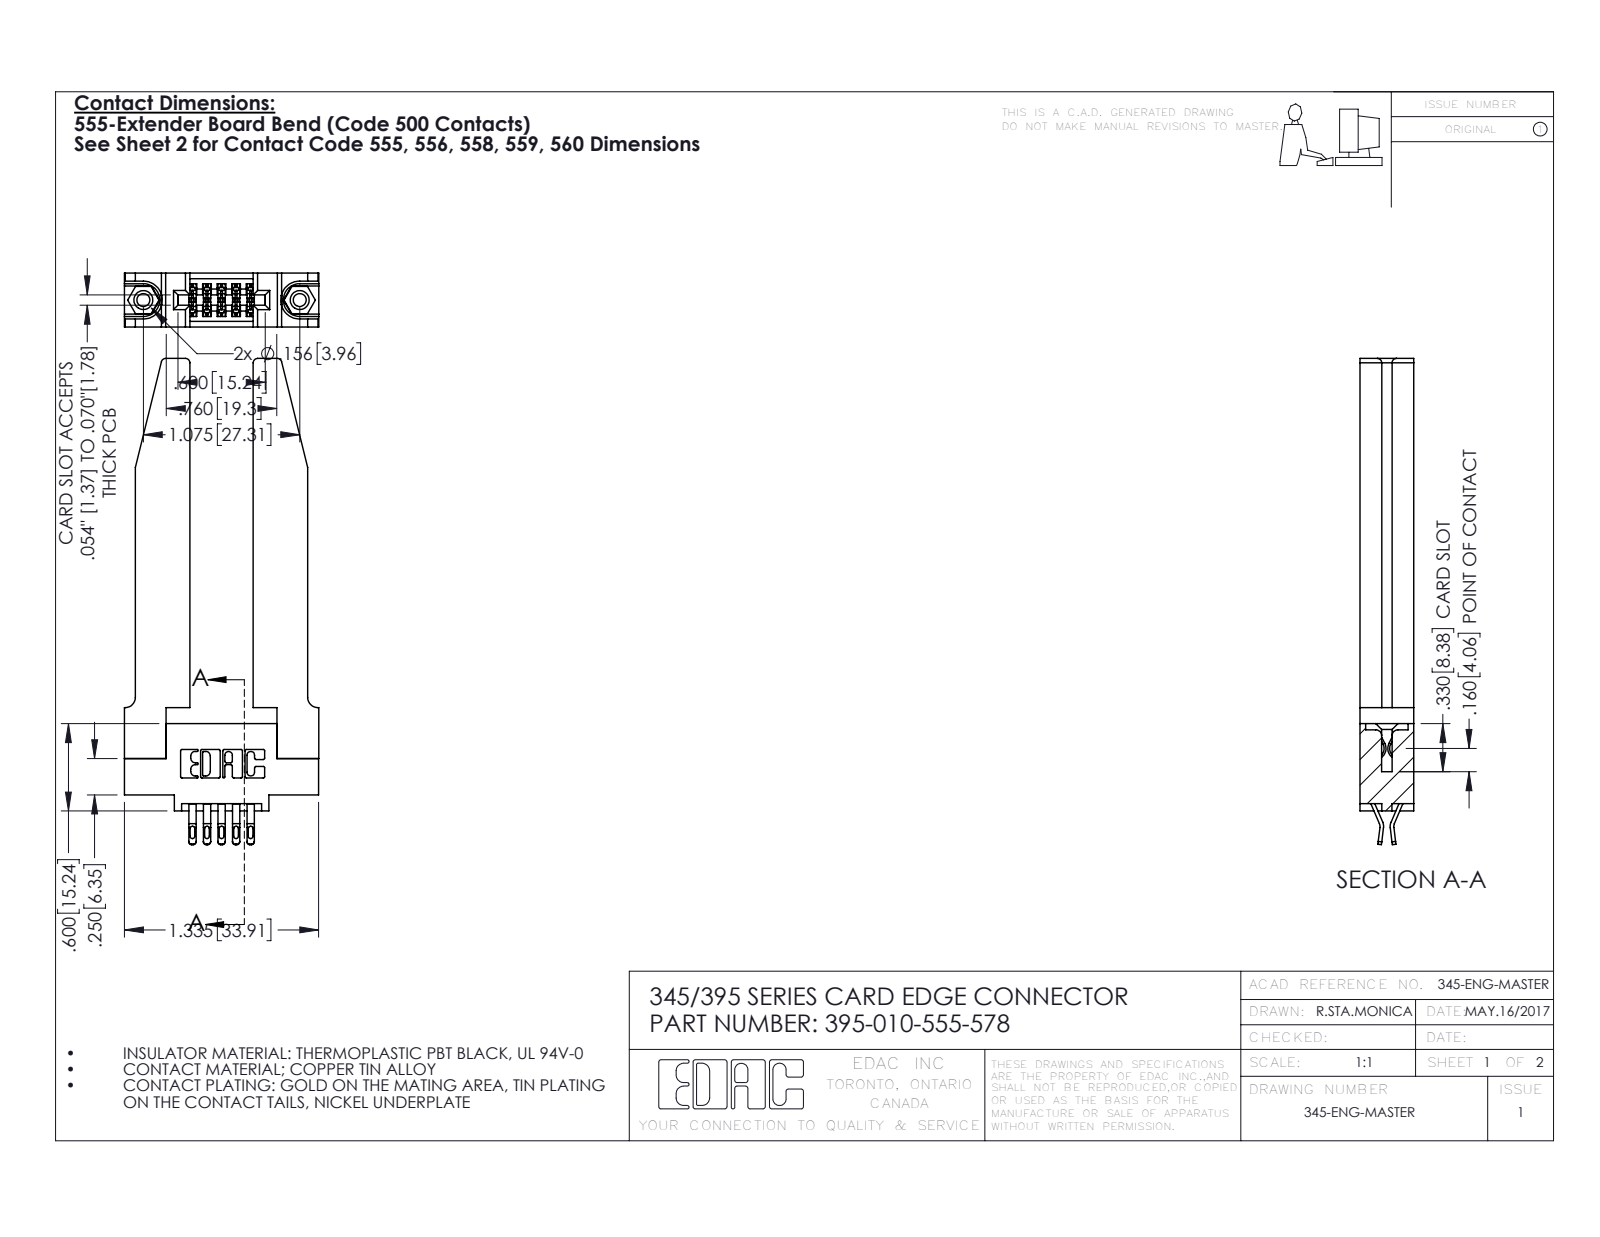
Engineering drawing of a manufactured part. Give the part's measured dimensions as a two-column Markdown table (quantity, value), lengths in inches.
| quantity | value |
| --- | --- |
| part name | 395-010-555-578; 345-220-078_345-220-078; 345-250-001_345-250-001-102; 345 Part_0.110 Offset - 0.156 Dia-TH (+1 more) |
| STEP written by | SolidWorks 2016 (CONFIG_CONTROL_DESIGN) |
| units | inches |
| bodies | 15 solids, 924 faces (536 planar, 336 cylindrical, 52 other) |
| overall size | 3.342 × 1.336 × 0.37 |
| volume | 0.652 in³ |
| surface area | 16.45 in² |
| round holes (diameter × count) | 0.089 × 2, 0.125 × 2, 0.156 × 2, 0.064 × 1 |
| round bosses / shafts (diameter × count) | 0.155 × 2 |
| partial cylindrical surfaces (radius × count) | 0.016 × 25, 0.01 × 22, 0.02 × 20, 0.006 × 15, 0.03 × 8, 0.007 × 6, 0.031 × 6, 0.026 × 3 |
| main face-to-face distances | 0.37, 0.15, 0.22, 0.435, 0.072, 0.148, 0.298, 0.077, 0.071, 0.2 |
| hole center spacings | 0.27, 0.847, 1.075 |
